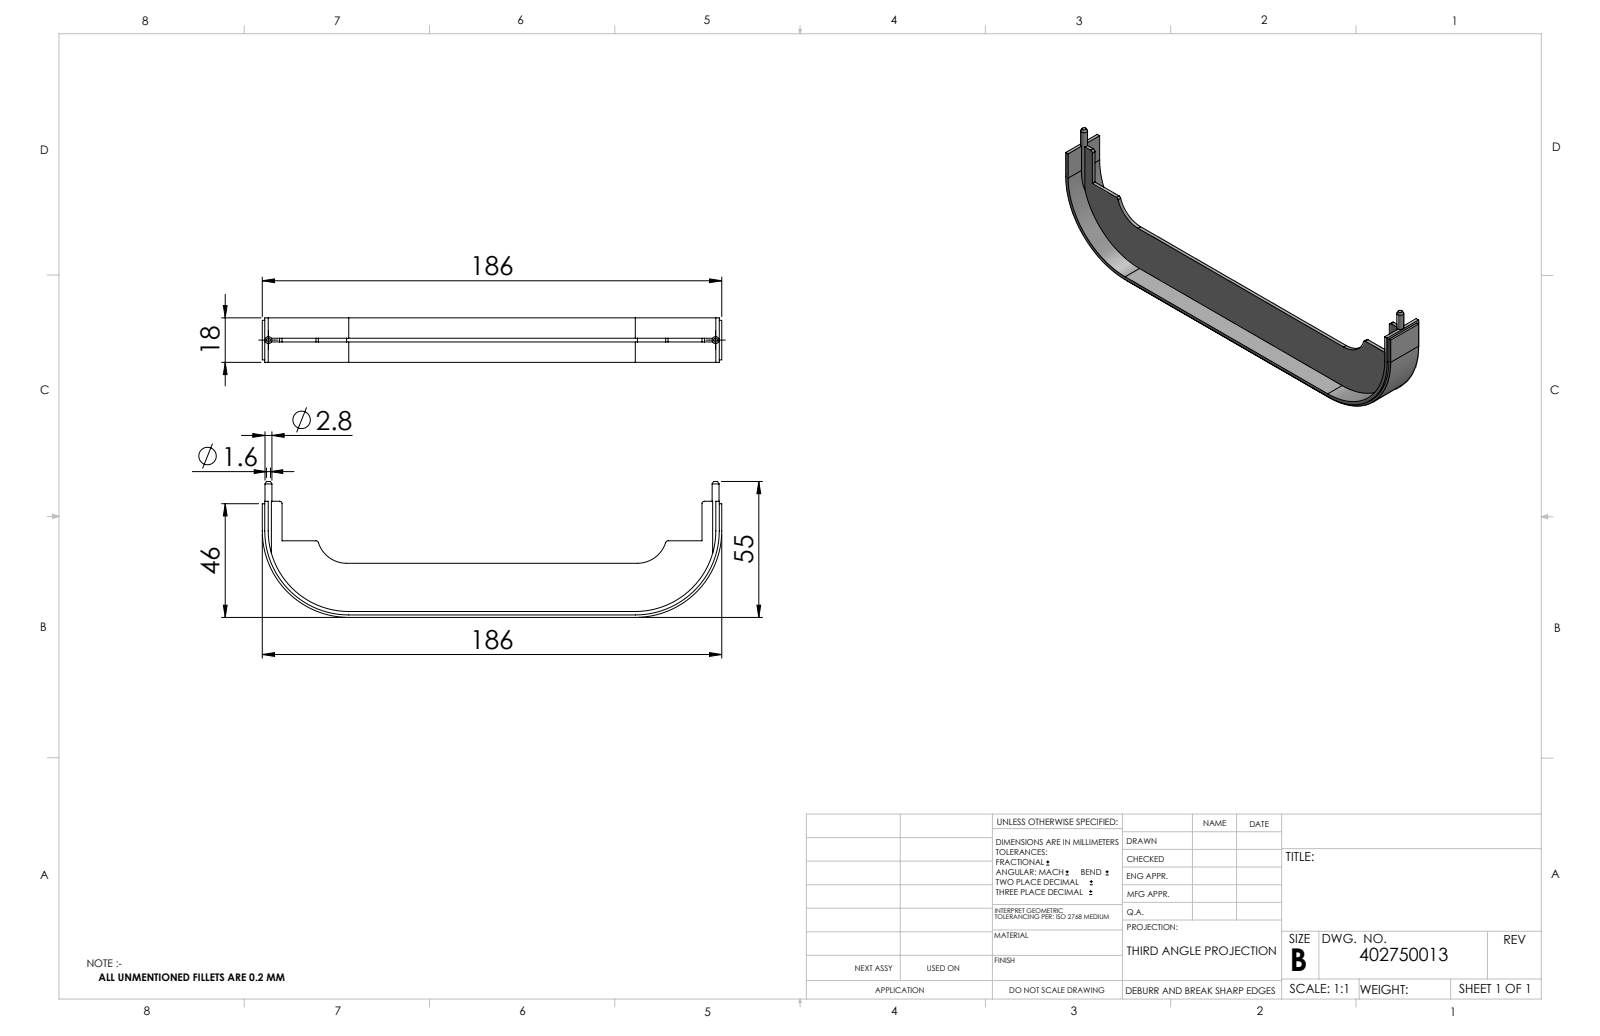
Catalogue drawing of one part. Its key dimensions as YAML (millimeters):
part_name: "402750013_c_1"
step_written_by: "SolidWorks 2014 (CONFIG_CONTROL_DESIGN)"
units: millimeters
bodies: {solids: 1, faces: 56, planar: 32, cylindrical: 20, other: 4}
overall_size: [186, 55, 18]
volume: 15757
surface_area: 17537
round_bosses_or_shafts:
  - {diameter: 2.8, count: 2}
partial_cylinders:
  - {radius: 1, count: 4}
  - {radius: 12, count: 2}
  - {radius: 32.6, count: 2}
  - {radius: 34, count: 2}
  - {radius: 35, count: 2}
face_to_face_distances: [1.5, 2.4, 1, 8.25, 9.75, 17, 7.25, 8.75, 183.6, 18]
